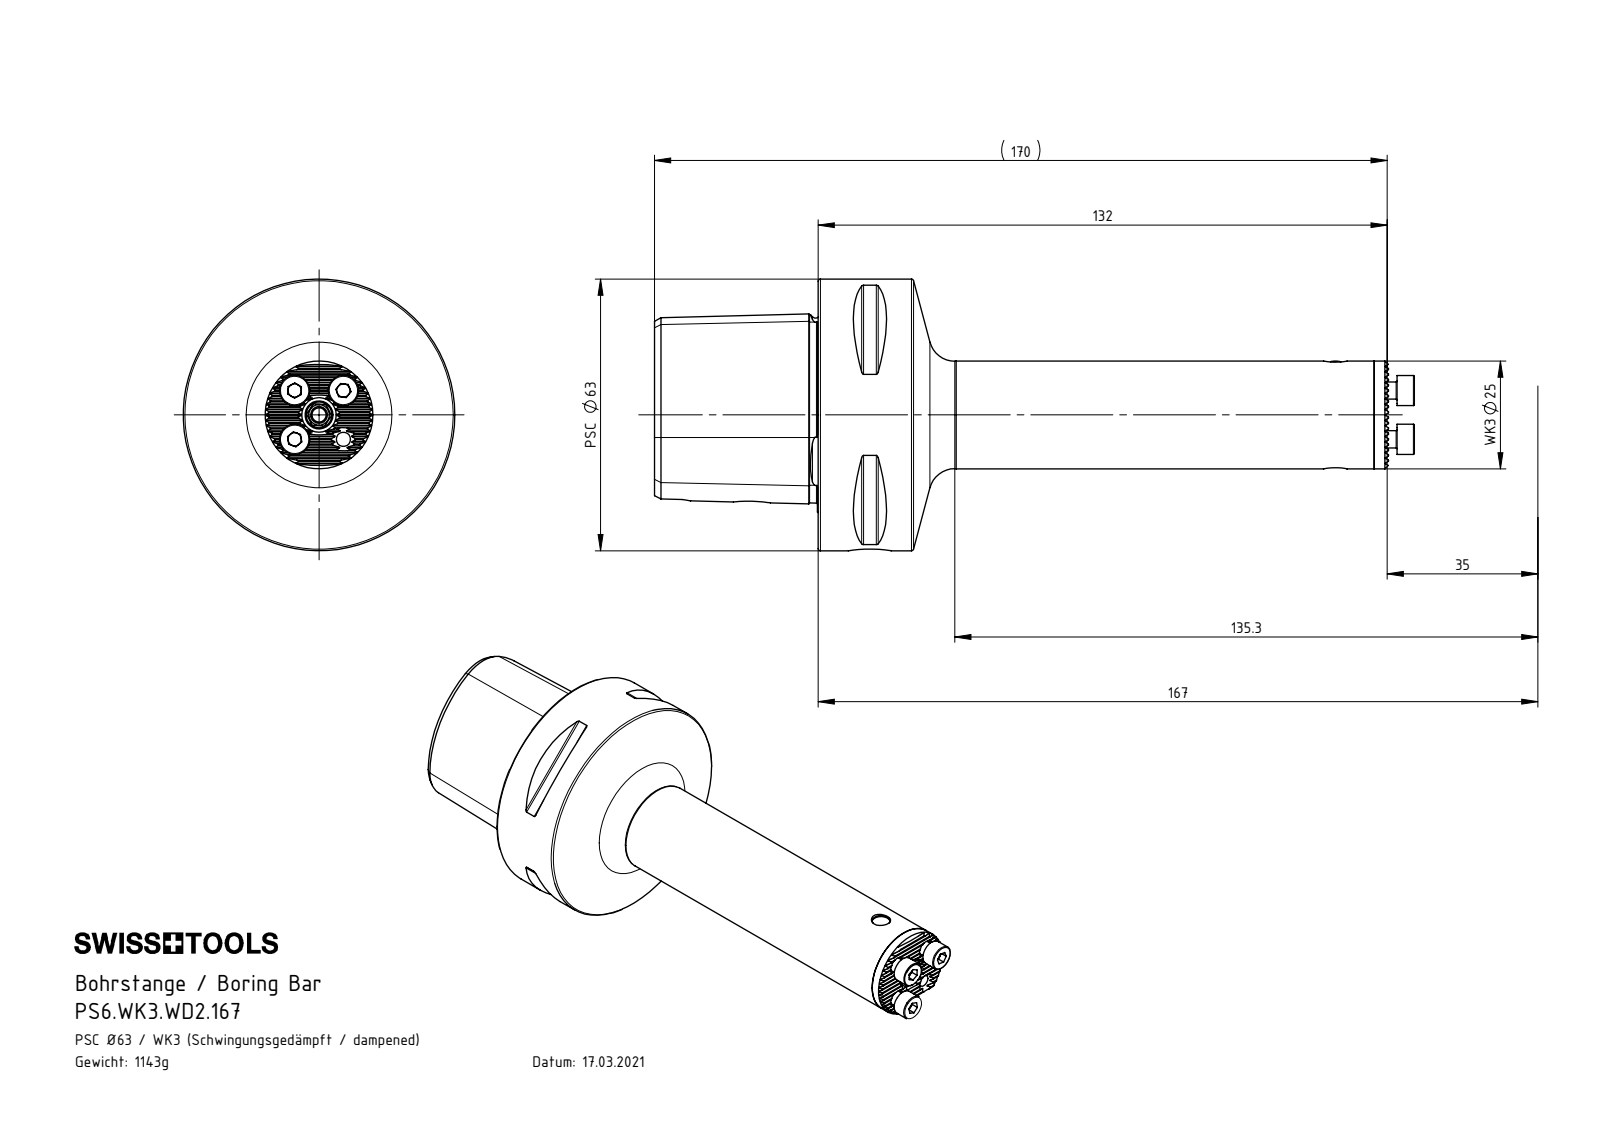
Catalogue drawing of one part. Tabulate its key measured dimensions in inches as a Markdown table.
| quantity | value |
| --- | --- |
| part name | WD2-ER1.008.037_A; WD2-ER1.021.019_A; DIN 3771 - 10x4; WD2-ER1.020.042_A (+8 more) |
| STEP written by | SolidWorks 2017 (AUTOMOTIVE_DESIGN) |
| units | inches |
| bodies | 16 solids, 493 faces (237 planar, 110 cylindrical, 146 other) |
| overall size | 6.941 × 2.48 × 2.48 |
| volume | 9.048 in³ |
| surface area | 77.43 in² |
| round holes (diameter × count) | 0.13 × 5, 0.197 × 1, 0.217 × 1, 0.236 × 1, 0.256 × 1, 0.268 × 1, 0.291 × 1, 0.319 × 1, 0.354 × 1, 0.394 × 1, 0.402 × 1, 0.433 × 1 |
| round bosses / shafts (diameter × count) | 0.276 × 3, 0.157 × 3, 2.48 × 1, 0.984 × 1, 0.827 × 1, 0.815 × 1, 0.787 × 1, 0.701 × 1 |
| partial cylindrical surfaces (radius × count) | 0.005 × 19, 0.02 × 8, 0.236 × 1 |
| main face-to-face distances | 0.236, 1.496, 1.906, 0.126, 0.98, 0.17, 5.945, 4.449, 0.043, 0.362 |
| hole center spacings | 0.315, 0.446, 0.63, 1.083, 4.252, 5.335 |
